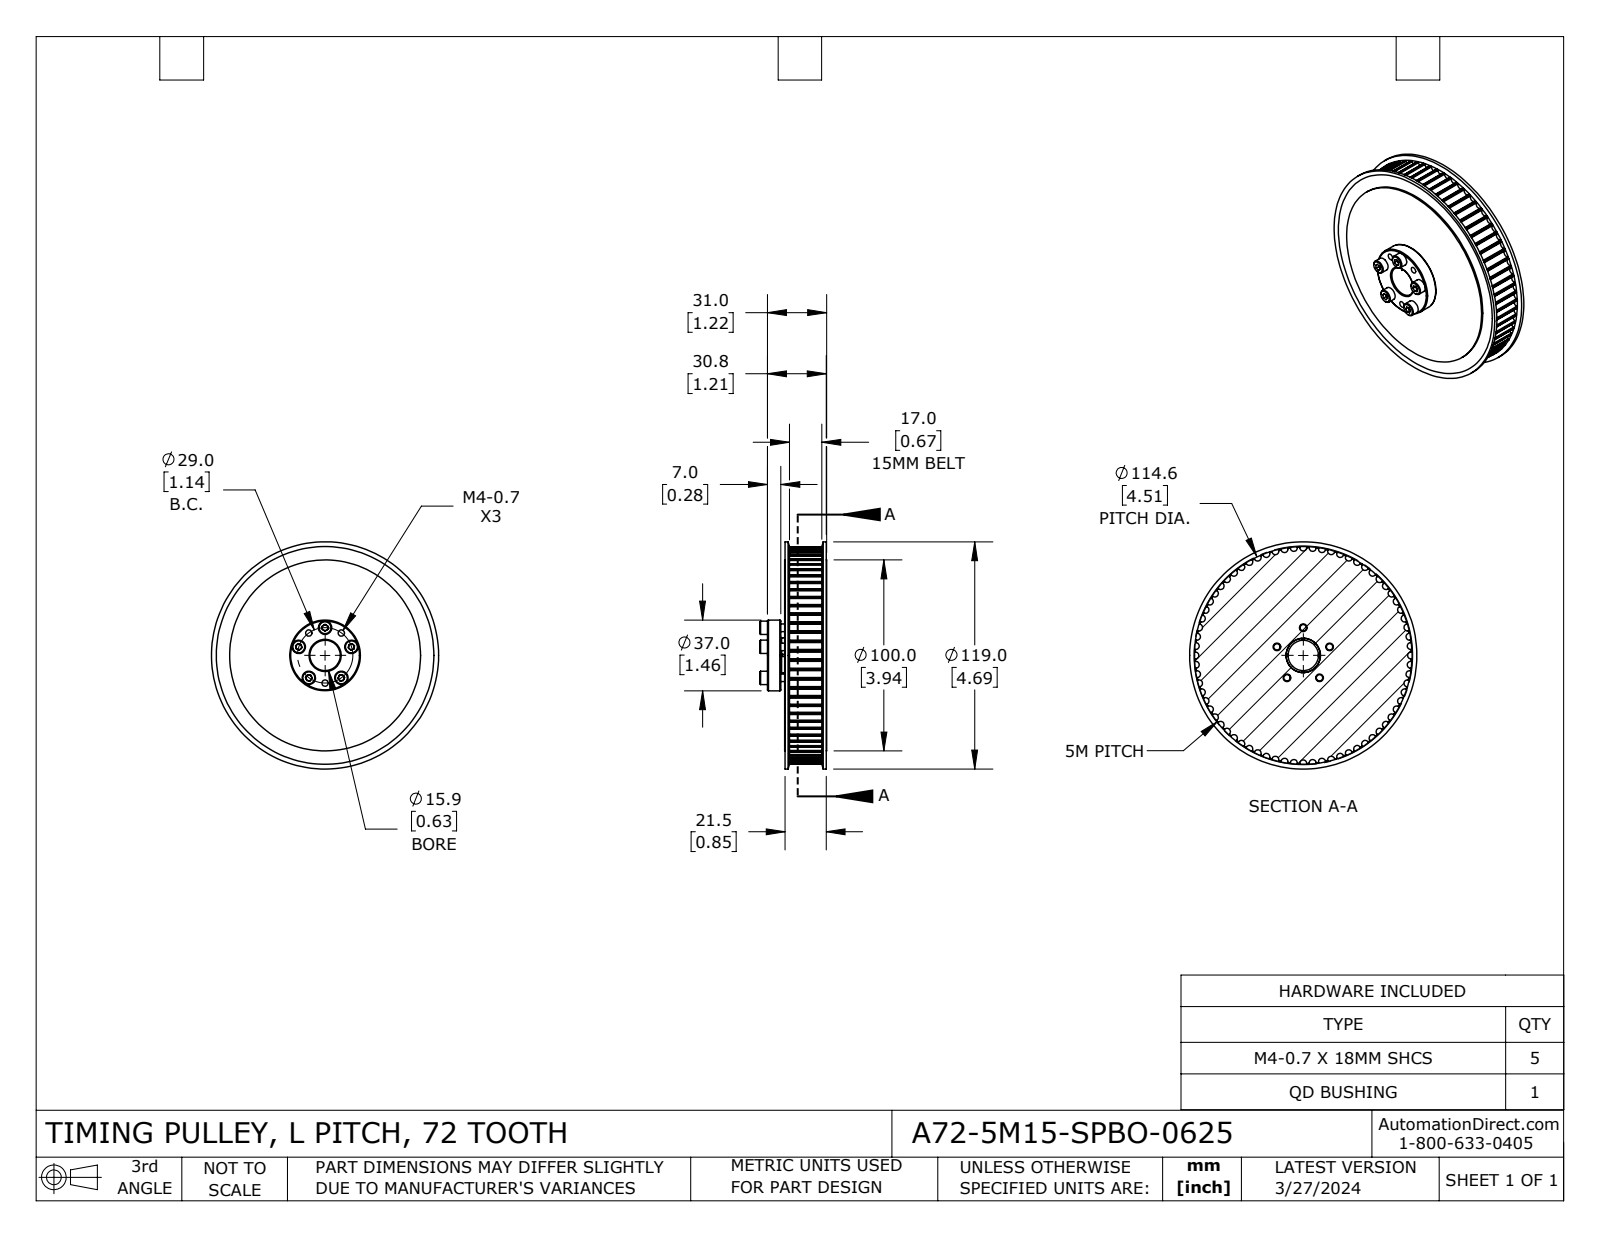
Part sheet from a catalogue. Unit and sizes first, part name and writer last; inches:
Units: inches
Overall size (bounding box): 4.685 × 4.685 × 1.378
Round holes (diameter × count): ⌀0.13 ×8, ⌀0.177 ×5, ⌀0.625 ×1, ⌀0.727 ×1, ⌀3.937 ×1
Round bosses / shafts (diameter × count): ⌀0.276 ×5, ⌀0.157 ×5, ⌀4.685 ×1, ⌀1.457 ×1
Partial cylindrical surfaces — rounded edges, fillets, slot ends (radius × count): R0.012 ×144, R0.072 ×72, R2.233 ×1
Main face-to-face distances: 0.098, 0.768, 0.866, 0.035, 0.831, 0.063, 0.732, 0.669, 0.795, 0.354
Hole centre spacings: 0.571, 1.086, 0.353, 0.924, 0.671, 1.142, 0.671
Volume: 13.21 in³ · Surface area: 82.94 in²
Bodies: 9 solids, 594 faces (101 planar, 427 cylindrical, 66 other)
Part name (STEP PRODUCT): A72-5M15-SPBO-0625
STEP written by: SolidWorks 2021 (CONFIG_CONTROL_DESIGN)
